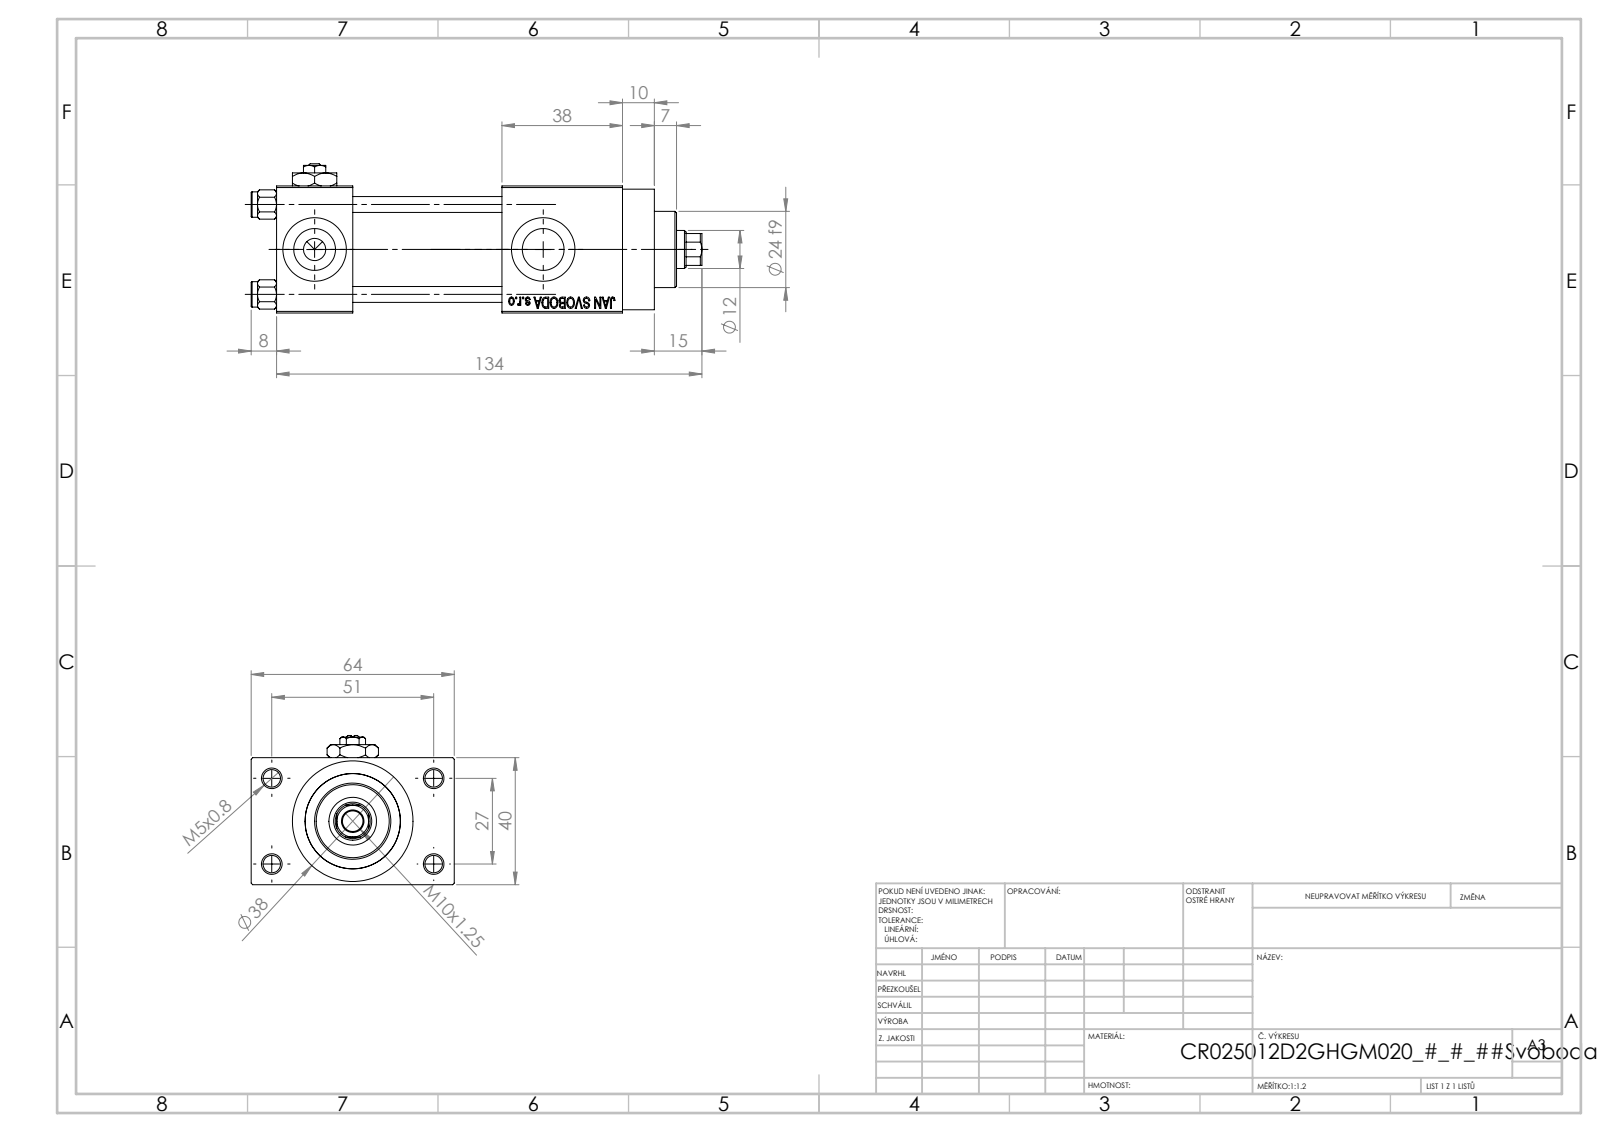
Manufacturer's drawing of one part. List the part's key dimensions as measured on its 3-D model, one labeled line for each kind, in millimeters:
Part name (STEP PRODUCT): NUT_M5_D; V215CR_D_Body; V215CR_D_TYCINKA; V215CR_VCP_D (+2 more)
STEP written by: SolidWorks 2019 (CONFIG_CONTROL_DESIGN)
Units: millimetres
Bodies: 12 solids, 1154 faces (519 planar, 95 cylindrical, 540 other)
Overall size (bounding box): 142 × 64 × 47
Volume: 172 605 mm³ · Surface area: 63 244 mm²
Round holes (diameter × count): ⌀5 ×4, ⌀5.5 ×4, ⌀20 ×4, ⌀7 ×3, ⌀13.16 ×3, ⌀6.5 ×1, ⌀12 ×1, ⌀15 ×1, ⌀25 ×1, ⌀30 ×1
Round bosses / shafts (diameter × count): ⌀8 ×4, ⌀38 ×1, ⌀31 ×1, ⌀24 ×1
Partial cylindrical surfaces — rounded edges, fillets, slot ends (radius × count): R5.5 ×1
Main face-to-face distances: 40, 12, 47, 52, 24, 71, 38, 109, 85, 64
Hole centre spacings: 11.37, 20.01, 28.3, 28.85, 29.89, 39.66, 48.34, 27
